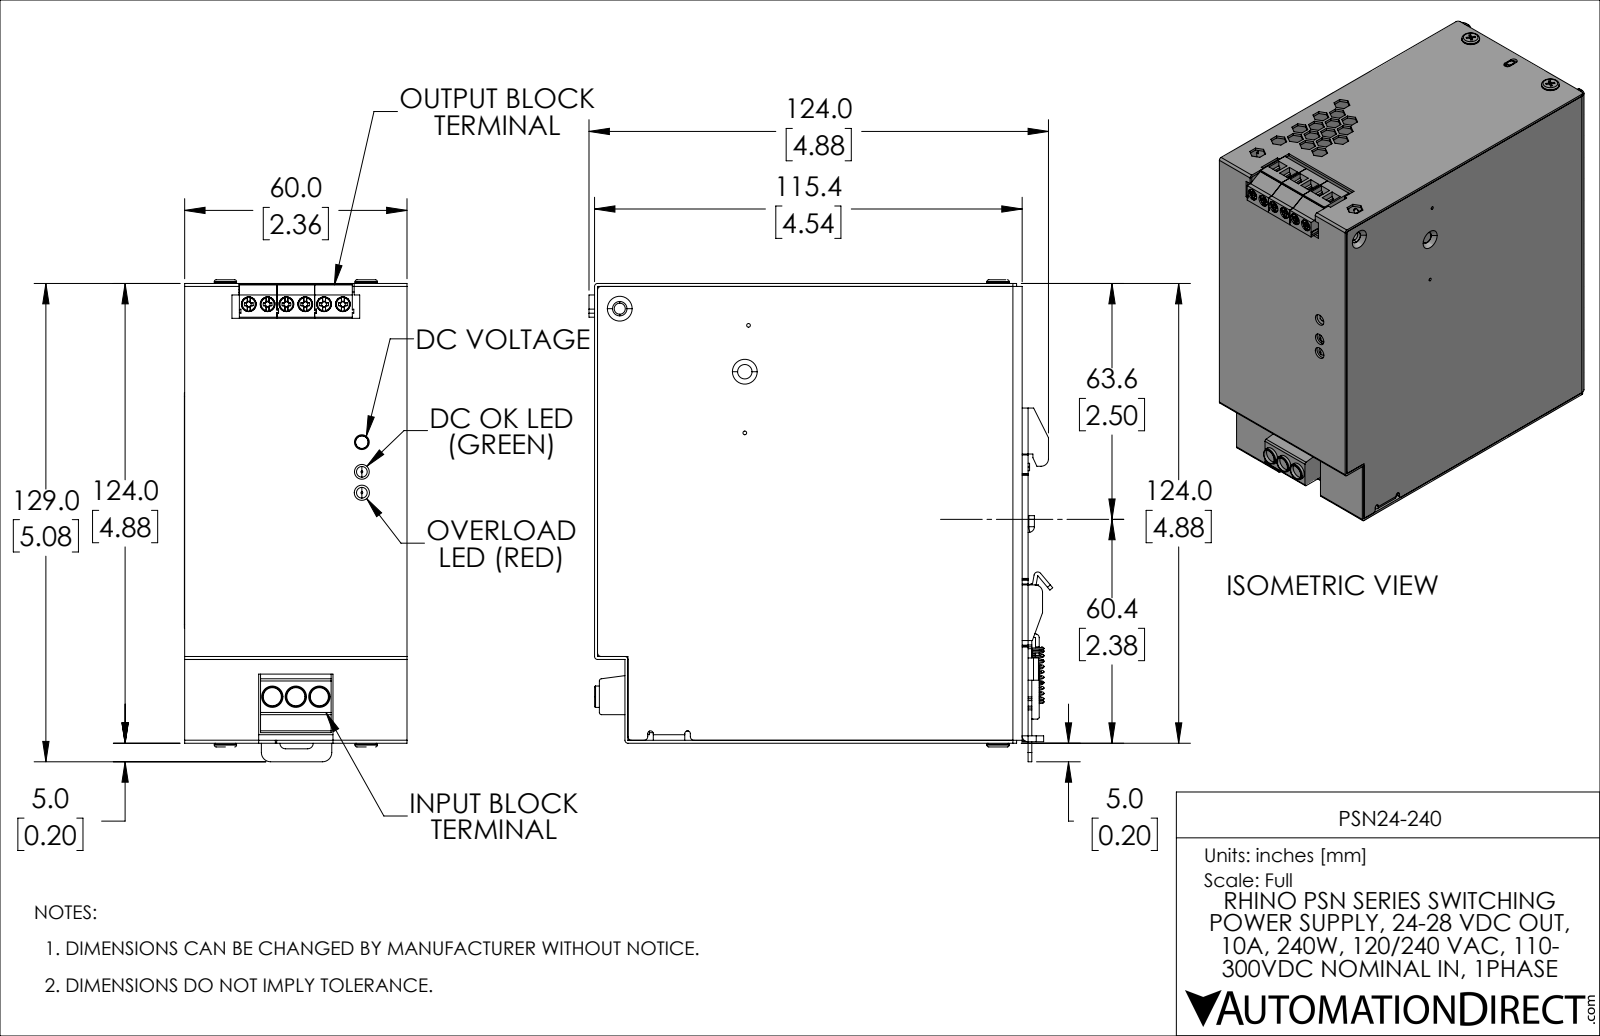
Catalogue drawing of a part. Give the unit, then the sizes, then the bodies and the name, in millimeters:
Units: millimetres
Overall size (bounding box): 130 × 125.1 × 60.1
Round holes (diameter × count): ⌀1 ×11, ⌀2.5 ×11, ⌀3.9 ×10, ⌀1.5 ×8, ⌀1.9 ×8, ⌀4 ×8, ⌀2 ×6, ⌀3.5 ×5, ⌀2.2 ×4, ⌀1.3 ×3, ⌀4.9 ×3, ⌀3.7 ×1
Round bosses / shafts (diameter × count): ⌀3.9 ×6, ⌀5.5 ×4, ⌀2 ×4, ⌀5.8 ×3, ⌀6 ×2, ⌀2.9 ×2, ⌀3.4 ×1
Partial cylindrical surfaces — rounded edges, fillets, slot ends (radius × count): R0.3 ×60, R1 ×43, R0.5 ×41, R0.1 ×24, R0.3 ×16, R0.8 ×12, R1.5 ×6, R1.6 ×6
Main face-to-face distances: 1.5, 58.5, 1.6, 0.8, 60, 57, 7.1, 5.5, 5.6, 51.4
Hole centre spacings: 5, 5.1, 7.7, 9.2, 73.3, 4.6, 10.2, 73.5
Volume: 116 000 mm³ · Surface area: 177 000 mm²
Bodies: 29 solids, 2058 faces (1388 planar, 493 cylindrical, 177 other)
Part name (STEP PRODUCT): PSN24-240
STEP written by: SolidWorks 2019 (AUTOMOTIVE_DESIGN)
